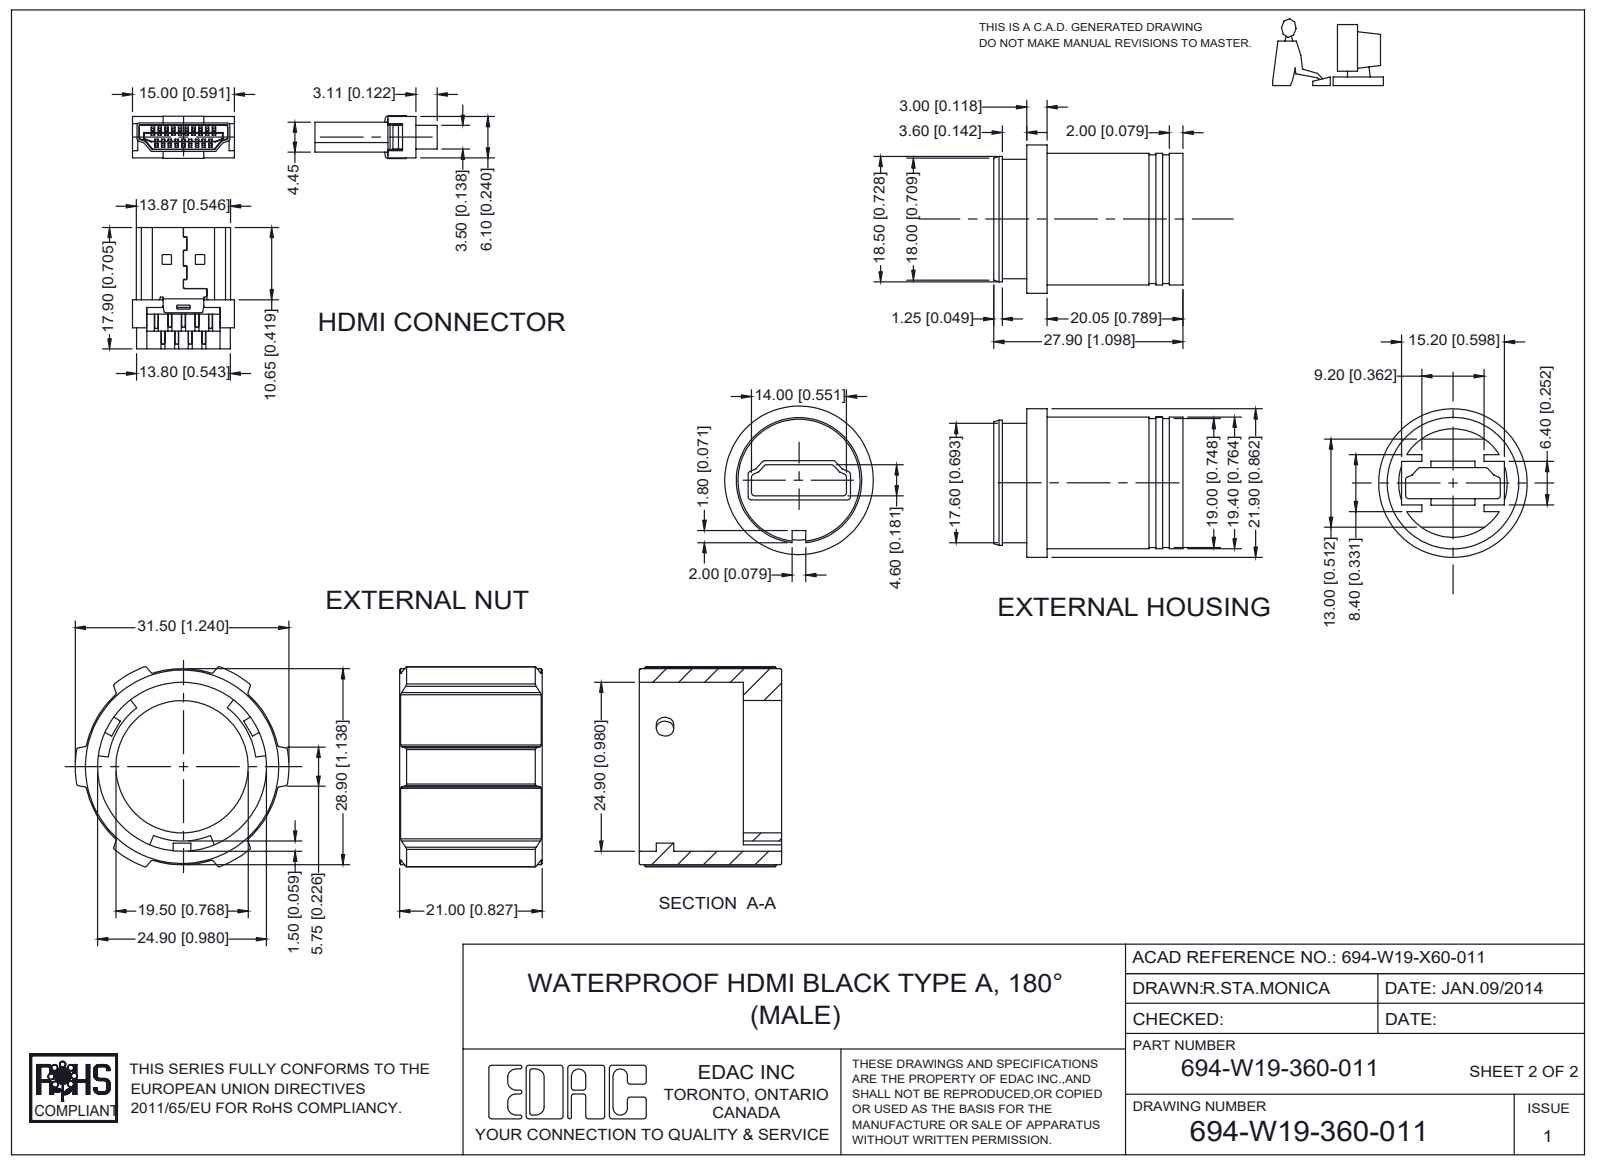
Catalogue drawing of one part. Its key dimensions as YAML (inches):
part_name: "694-W19-360-011; HDMI CONTACT3 694-W19-X60-011; HOUSING OUTER 694-W19-X60-011; O-RING 694-W19-X60-011 (+7 more)"
step_written_by: "SolidWorks 2020 (AUTOMOTIVE_DESIGN)"
units: inches
bodies: {solids: 25, faces: 2367, planar: 1591, cylindrical: 761, other: 15}
overall_size: [1.394, 1.24, 1.161]
volume: 0.603
surface_area: 19.68
round_holes:
  - {diameter: 0.628, count: 1}
  - {diameter: 0.673, count: 1}
  - {diameter: 0.768, count: 1}
  - {diameter: 0.98, count: 1}
round_bosses_or_shafts:
  - {diameter: 0.86, count: 1}
  - {diameter: 0.846, count: 1}
  - {diameter: 0.761, count: 1}
  - {diameter: 0.746, count: 1}
  - {diameter: 0.726, count: 1}
  - {diameter: 0.691, count: 1}
partial_cylinders:
  - {radius: 0.006, count: 284}
  - {radius: 0.004, count: 114}
  - {radius: 0.012, count: 29}
  - {radius: 0.02, count: 26}
  - {radius: 0.006, count: 19}
  - {radius: 0.008, count: 18}
  - {radius: 0.004, count: 10}
  - {radius: 0.007, count: 10}
face_to_face_distances: [0.016, 0.039, 0.118, 0.065, 0.341, 0.094, 0.222, 0.36, 0.291, 0.531]
